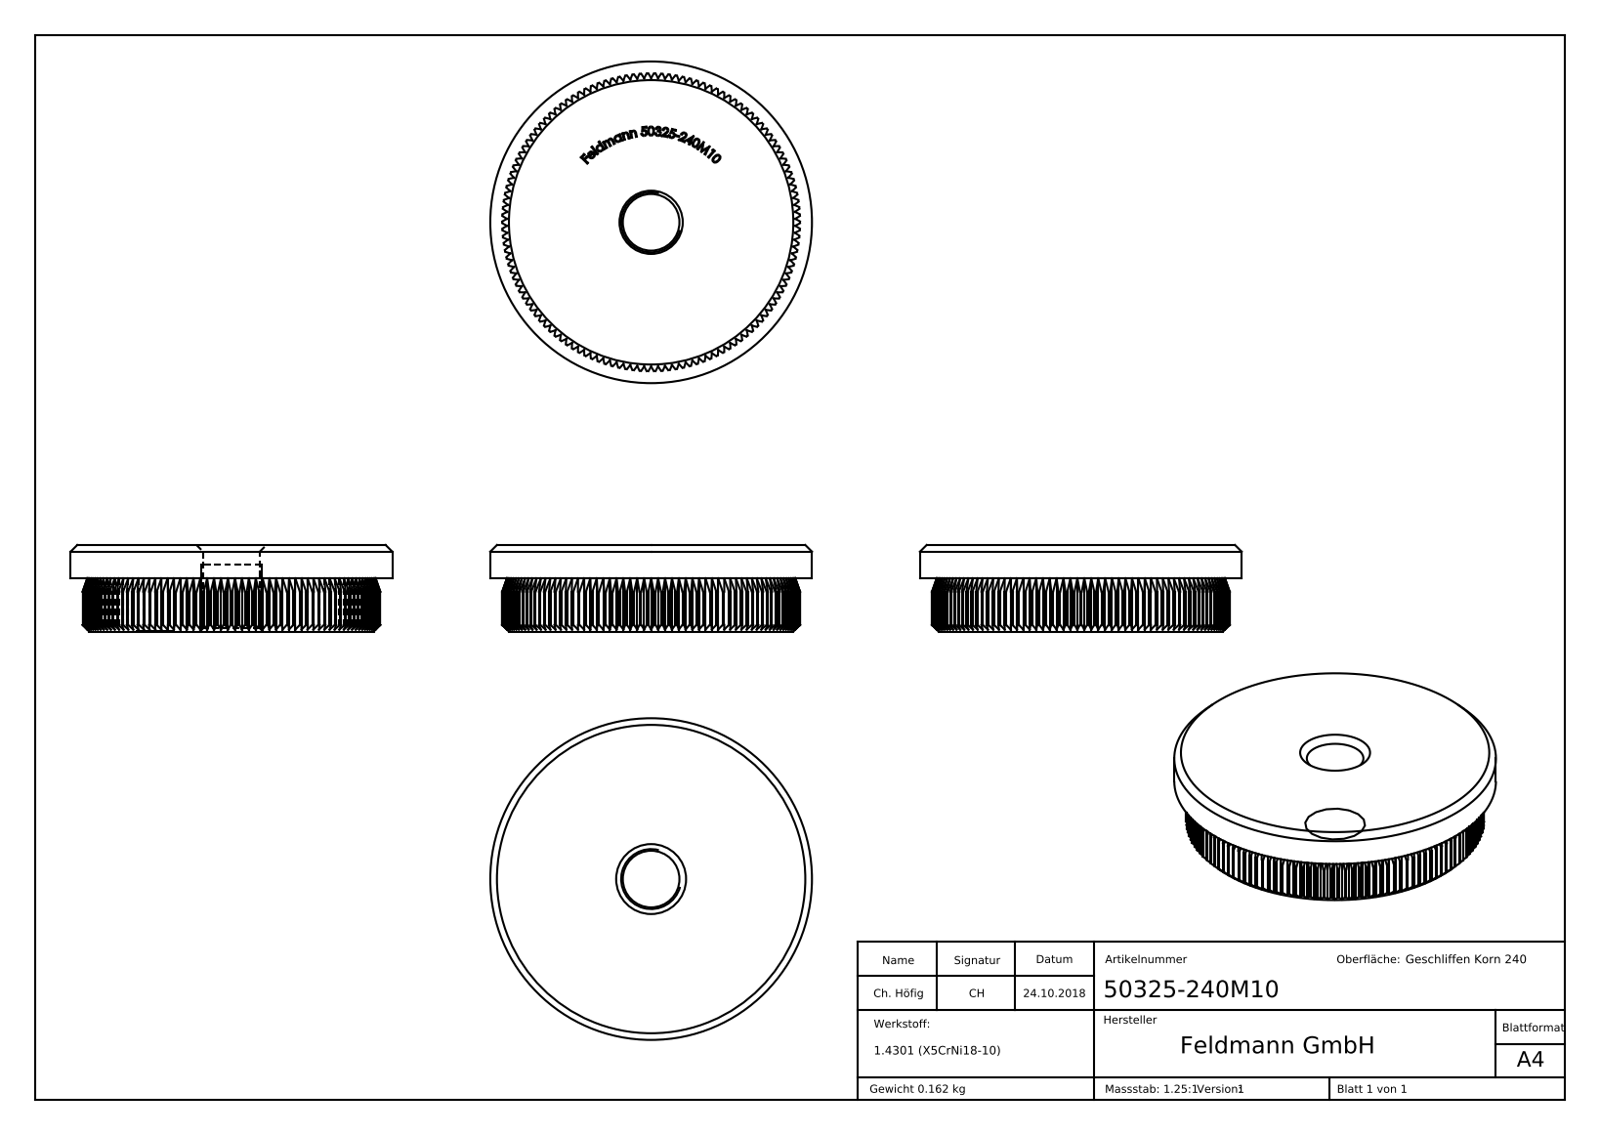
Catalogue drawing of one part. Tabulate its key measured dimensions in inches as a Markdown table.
| quantity | value |
| --- | --- |
| part name | 50325-240M10 |
| STEP written by | SolidWorks 2015 (CONFIG_CONTROL_DESIGN) |
| units | inches |
| bodies | 1 solid, 821 faces (410 planar, 134 cylindrical, 277 other) |
| overall size | 1.902 × 1.902 × 0.512 |
| volume | 1.251 in³ |
| surface area | 9.839 in² |
| round holes (diameter × count) | 0.335 × 1 |
| round bosses / shafts (diameter × count) | 1.902 × 1 |
| partial cylindrical surfaces (radius × count) | 0.88 × 1 |
| main face-to-face distances | 0.512, 0.315, 0.197, 0.853, 0.852, 0.854, 0.851, 0.311, 0.508, 0.021 |
